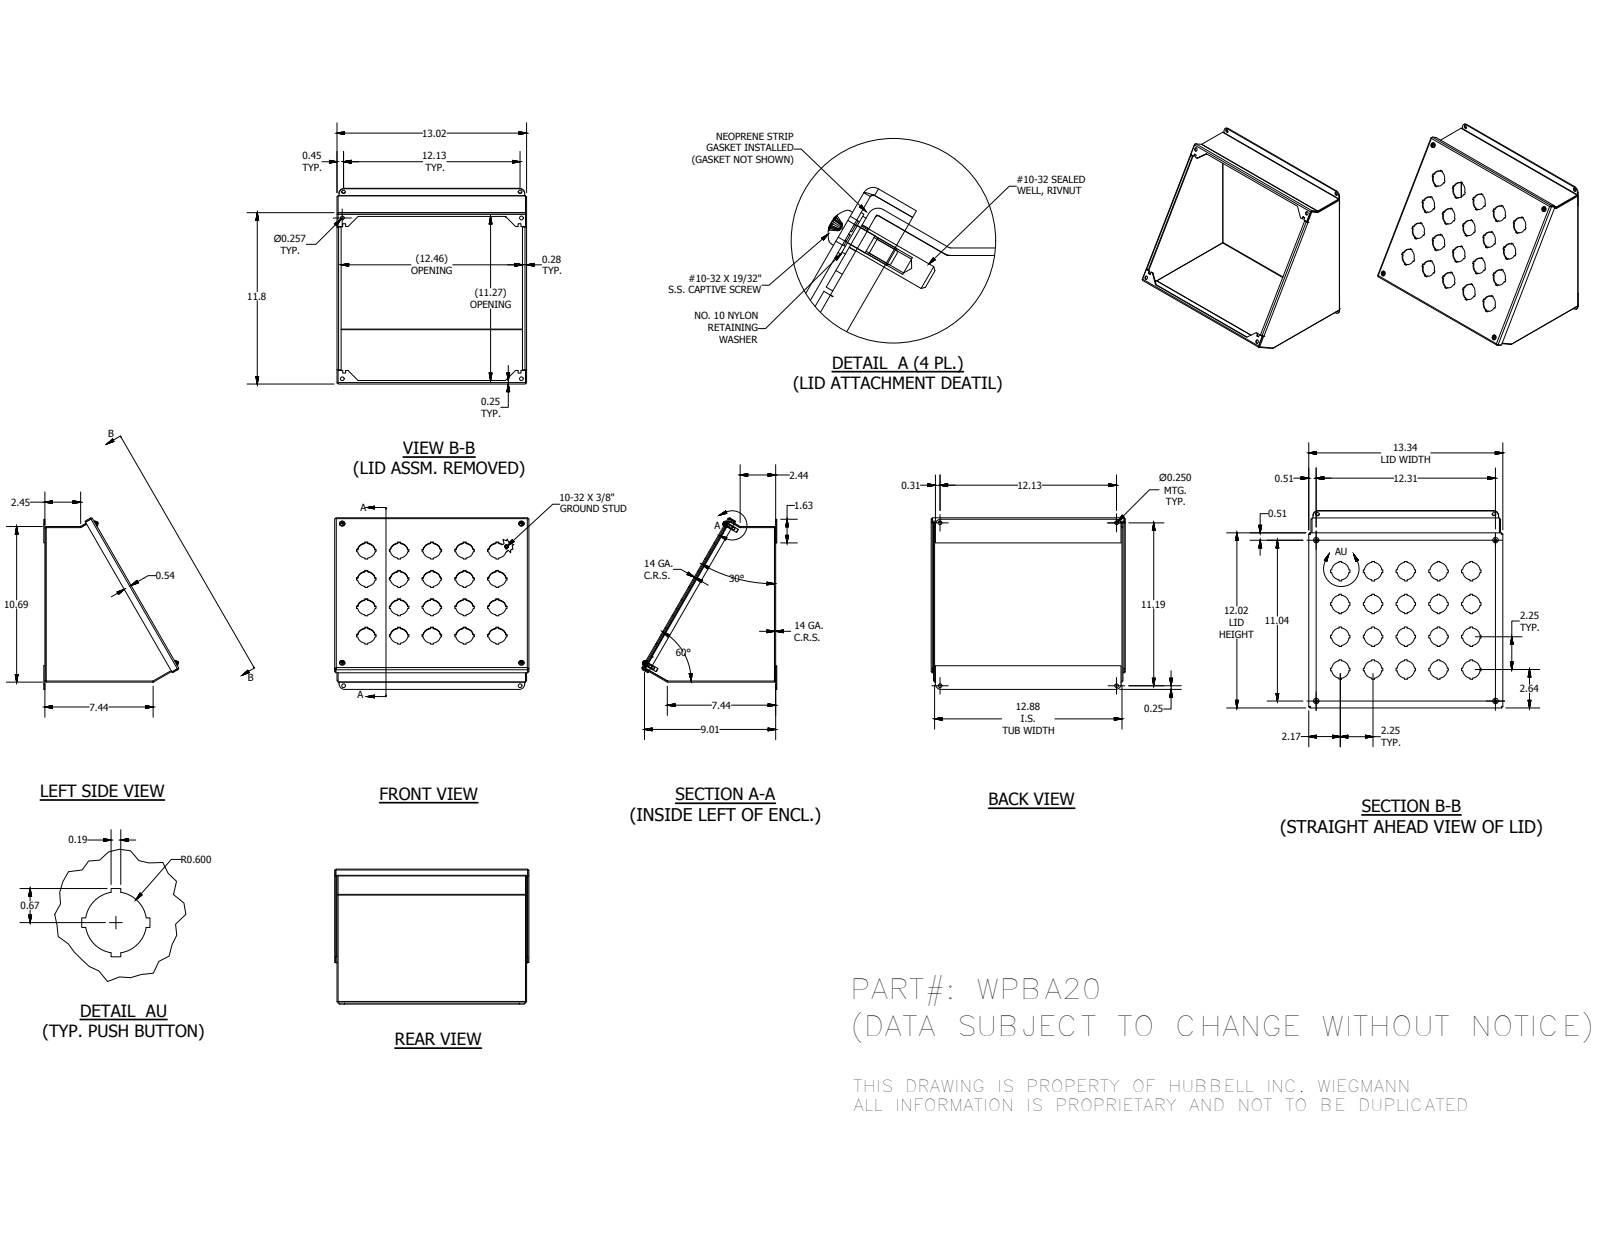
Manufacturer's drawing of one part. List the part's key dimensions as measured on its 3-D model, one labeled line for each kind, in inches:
Part name (STEP PRODUCT): WPBA20BKP; WPBA4ROWEWPR; WPBA4ROWEWPL; 34984 (+6 more)
STEP written by: Autodesk Inventor 2014 (AUTOMOTIVE_DESIGN)
Units: inches
Bodies: 19 solids, 800 faces (531 planar, 170 cylindrical, 99 other)
Overall size (bounding box): 13.337 × 11.783 × 9.266
Volume: 47.57 in³ · Surface area: 1 315 in²
Round holes (diameter × count): ⌀1.2 ×20, ⌀0.156 ×4, ⌀0.196 ×4, ⌀0.25 ×4, ⌀0.257 ×4, ⌀0.278 ×4, ⌀0.281 ×4
Round bosses / shafts (diameter × count): ⌀0.19 ×5, ⌀0.453 ×4, ⌀0.406 ×4, ⌀0.373 ×4, ⌀0.248 ×4, ⌀0.25 ×1
Partial cylindrical surfaces — rounded edges, fillets, slot ends (radius × count): R0.031 ×12, R0.105 ×12, R0.089 ×4, R0.375 ×4
Main face-to-face distances: 0.074, 12.949, 12.949, 12.875, 13.023, 0.074, 10.616, 0.148, 10.542, 10.69
Hole centre spacings: 5.031, 2.25, 4.5, 3.182, 6.75, 7.115, 8.113, 3.182
